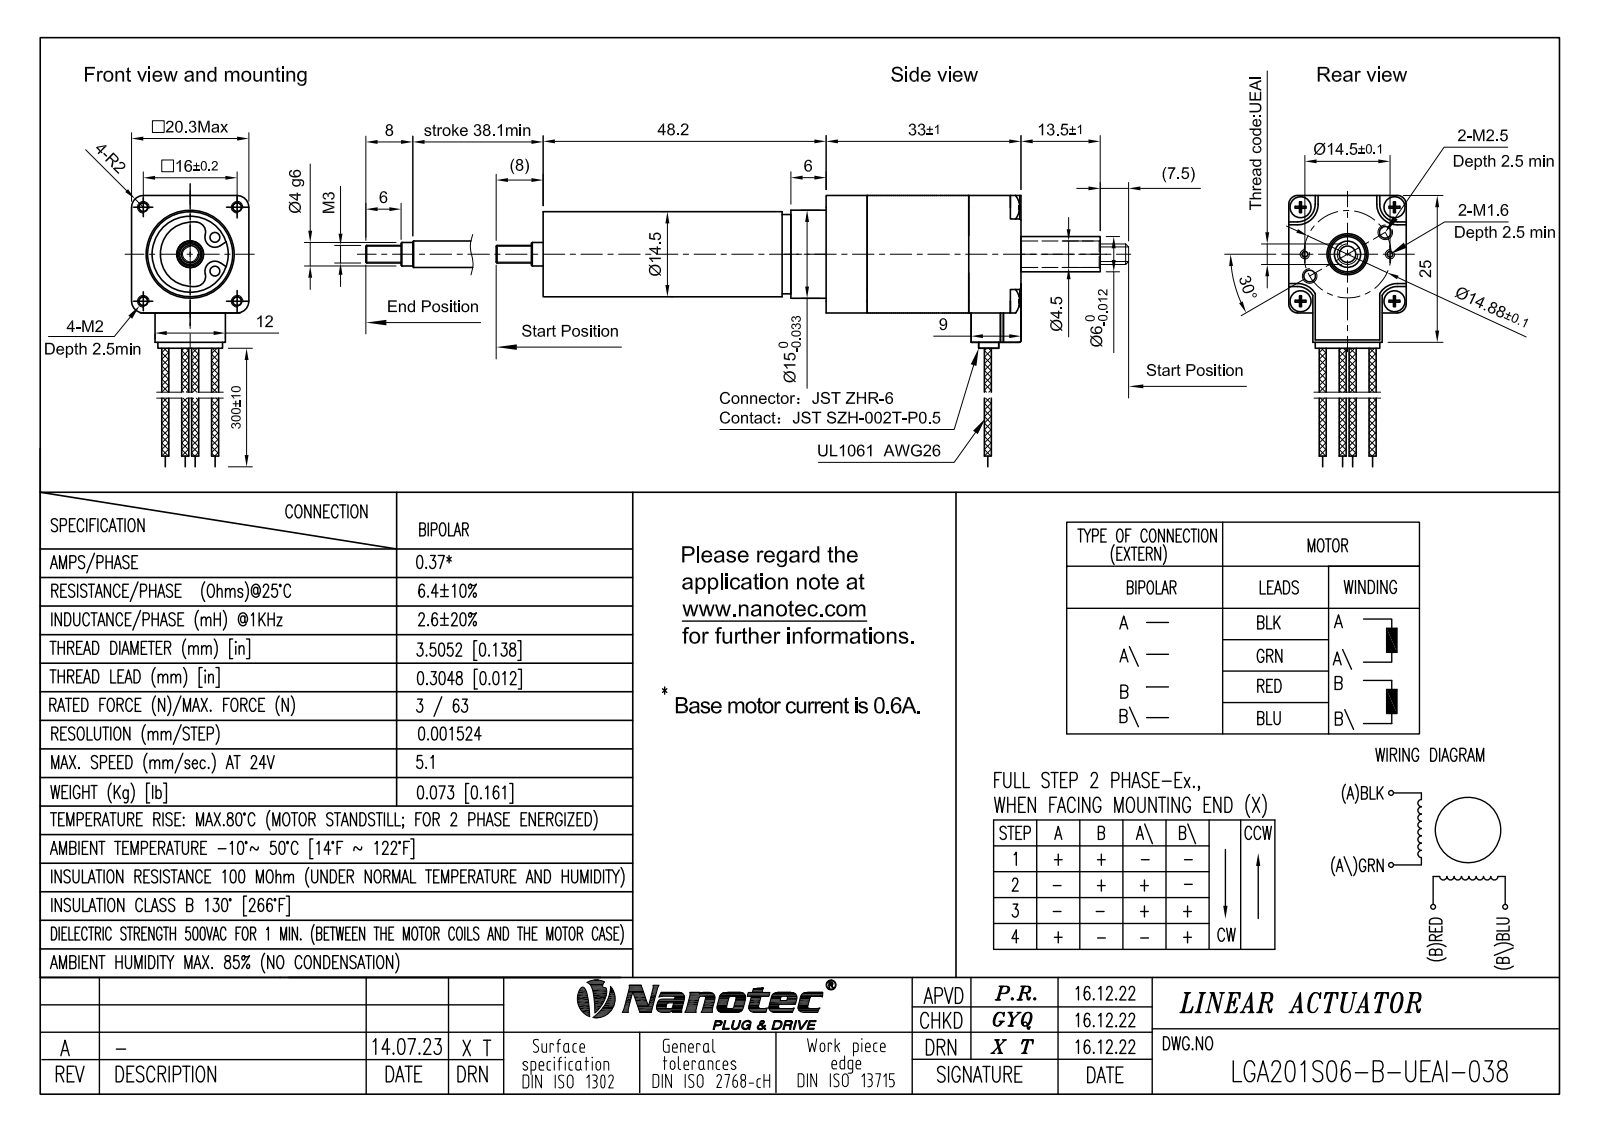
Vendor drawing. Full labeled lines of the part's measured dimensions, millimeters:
Part name (STEP PRODUCT): 零件2
STEP written by: Autodesk Inventor 2013 (CONFIG_CONTROL_DESIGN)
Units: millimetres
Bodies: 1 solid, 302 faces (157 planar, 63 cylindrical, 82 other)
Overall size (bounding box): 135.7 × 25 × 20
Volume: 21 680 mm³ · Surface area: 8 166 mm²
Round holes (diameter × count): ⌀0.6 ×6, ⌀1.6 ×4, ⌀1.22 ×2, ⌀1.7 ×2, ⌀4.5 ×1, ⌀6.5 ×1, ⌀13 ×1
Round bosses / shafts (diameter × count): ⌀0.5 ×12, ⌀15 ×1, ⌀14.5 ×1, ⌀13.5 ×1, ⌀6 ×1, ⌀4 ×1, ⌀3.5 ×1, ⌀3 ×1
Partial cylindrical surfaces — rounded edges, fillets, slot ends (radius × count): R1.7 ×4, R2 ×4, R5.53 ×1, R6.8 ×1
Main face-to-face distances: 20, 33.2, 46.1, 5, 25, 79.3, 16, 9, 3.5, 29.7
Hole centre spacings: 1.5, 3, 8.04, 11.31, 16, 17.22, 4.5, 10.64
